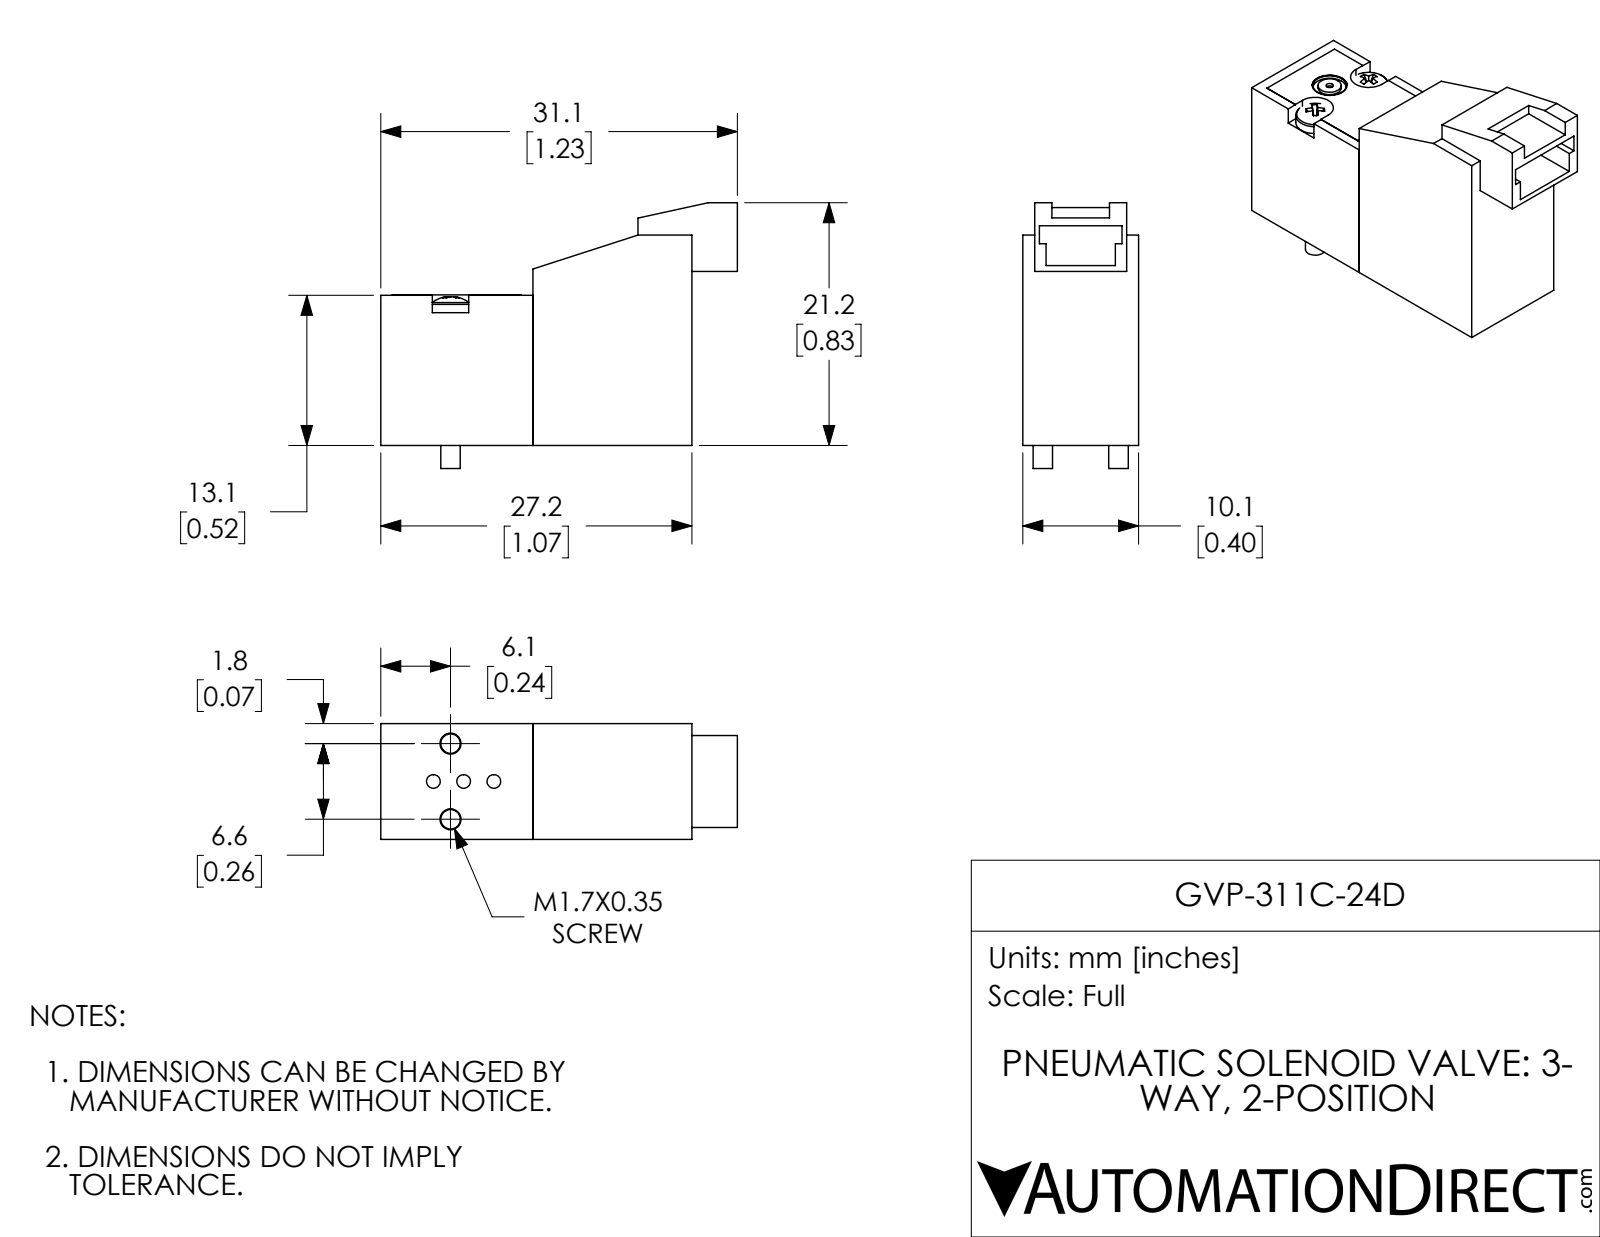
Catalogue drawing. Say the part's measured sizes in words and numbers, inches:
The part is named "GVP-311C-24D". Its 3-D file was written by "SolidWorks 2018 (AUTOMOTIVE_DESIGN)". It is 4 solids with 126 faces: 83 planar, 29 cylindrical and 14 other. Overall it measures 1.226 by 0.913 by 0.398 inches. Its volume is 0.259 cubic inches and its surface area 4.199 square inches. Round holes: 3 of diameter 0.047, 2 of diameter 0.072, 1 of diameter 0.025, 1 of diameter 0.115, 1 of diameter 0.12. Round bosses or shafts: 2 of diameter 0.134, 2 of diameter 0.067, 1 of diameter 0.08. Partial cylindrical surfaces (rounded edges, fillets, slot ends): 2 of radius 0.062. The main face-to-face distances are 0.398, 0.547, 1.07, 0.523, 0.517, 0.238, 0.041, 0.357, 0.755, 0.618. The hole center spacings are 0.104, 0.198, 0.105, 0.137, 0.138, 0.143, 0.143, 0.143.
